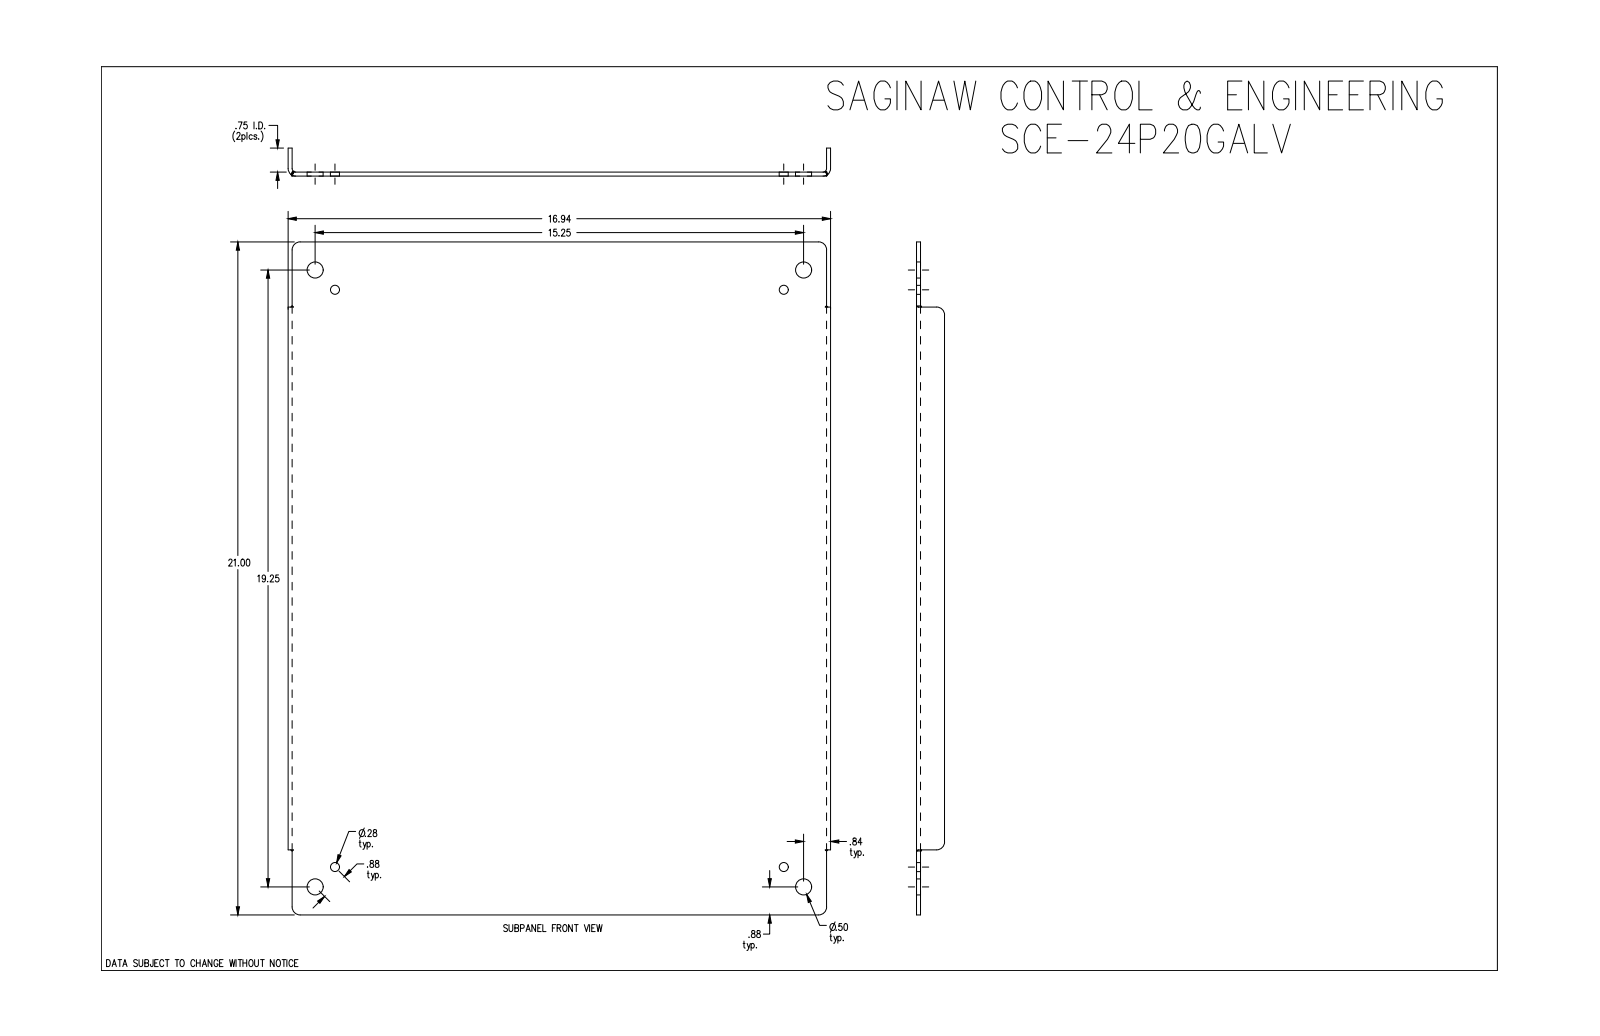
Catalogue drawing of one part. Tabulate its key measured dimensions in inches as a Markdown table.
| quantity | value |
| --- | --- |
| part name | SCE-24P20GALV |
| STEP written by | SolidWorks 2019 (CONFIG_CONTROL_DESIGN) |
| units | inches |
| bodies | 1 solid, 50 faces (18 planar, 20 cylindrical, 12 other) |
| overall size | 21 × 16.938 × 0.875 |
| volume | 47.05 in³ |
| surface area | 763.7 in² |
| round holes (diameter × count) | 0.281 × 4, 0.5 × 4 |
| partial cylindrical surfaces (radius × count) | 0.25 × 6, 0.112 × 2, 0.237 × 2 |
| main face-to-face distances | 0.125, 0.125, 16.813, 16.687, 16.938, 0.75, 0.875, 21, 2.031, 18.969 |
| hole center spacings | 0.875, 14.644, 18.641, 23.689, 14.013, 15.25, 18.013, 19.25 |
